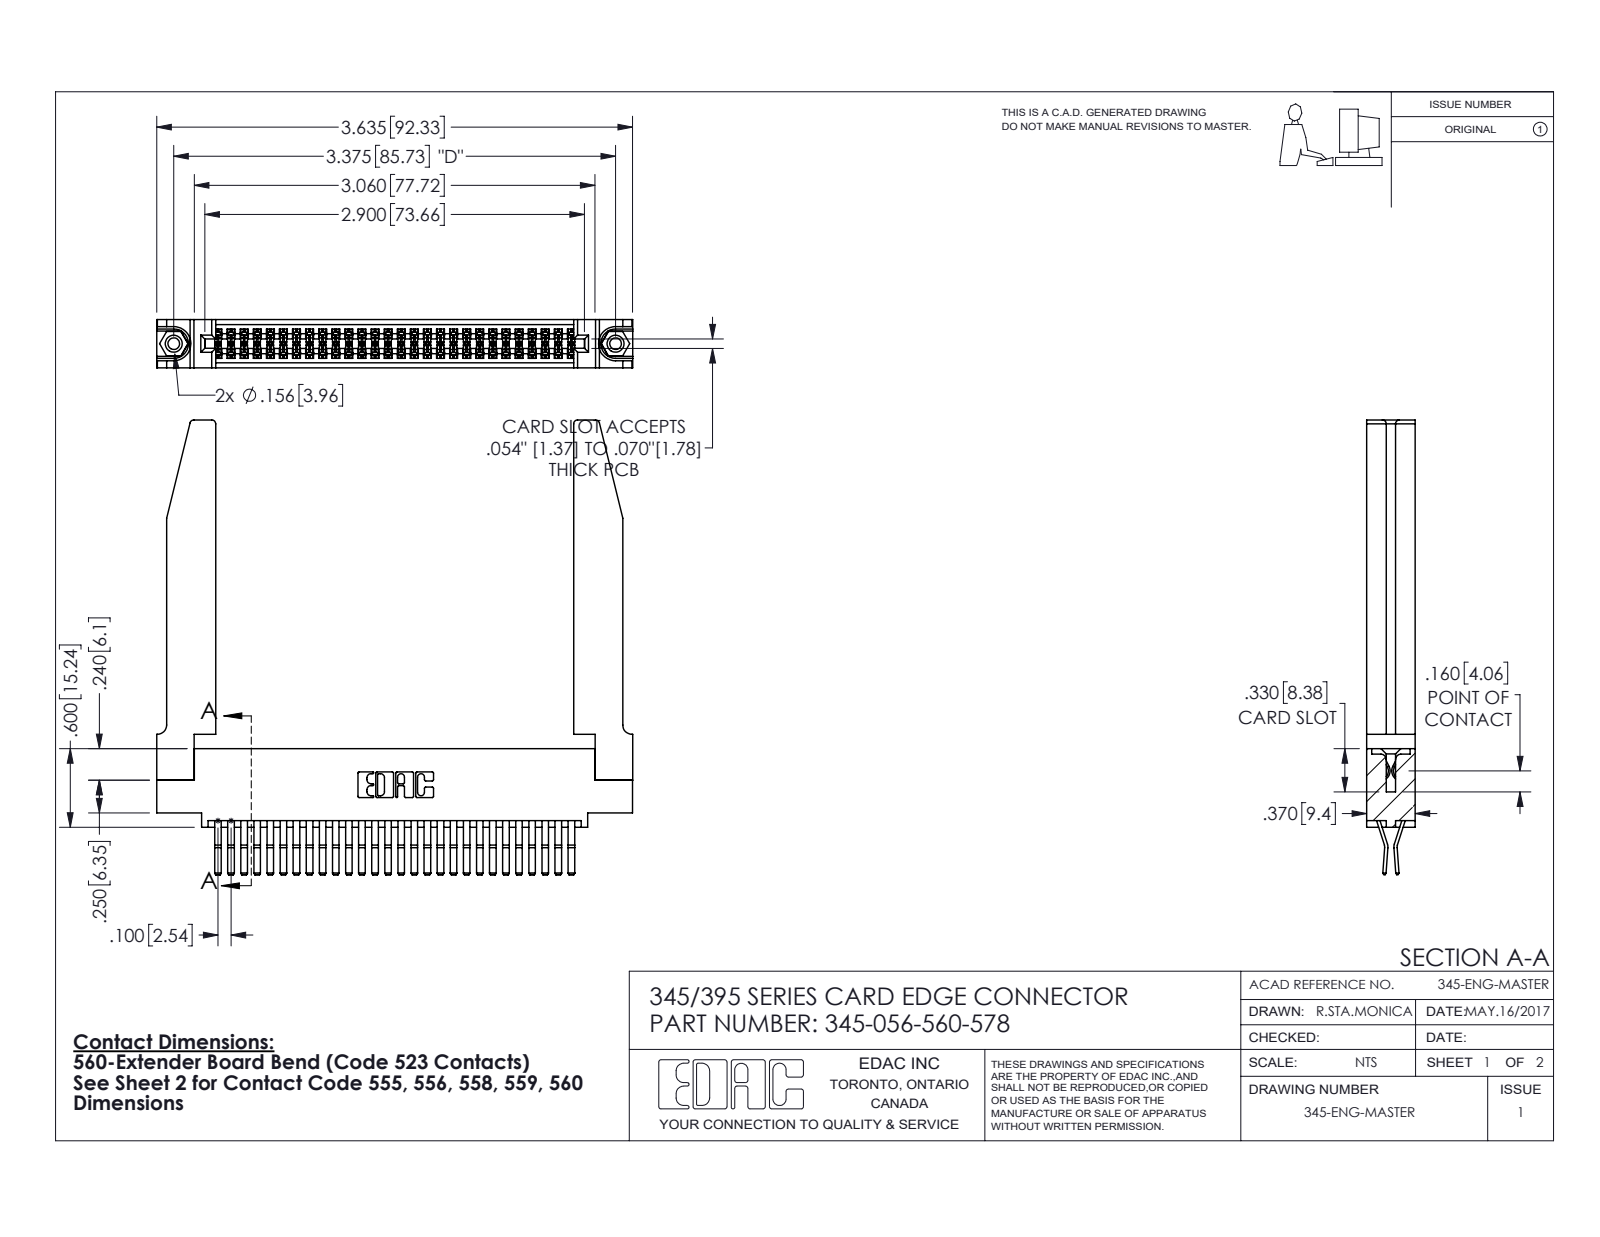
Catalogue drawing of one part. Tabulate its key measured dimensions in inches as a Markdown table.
| quantity | value |
| --- | --- |
| part name | 345-250-001_345-250-001-102; 345-220-078_345-220-078; 345-292-001_560 Tail; 345-056-560-578 (+1 more) |
| STEP written by | SolidWorks 2016 (CONFIG_CONTROL_DESIGN) |
| units | inches |
| bodies | 61 solids, 3276 faces (2074 planar, 1150 cylindrical, 52 other) |
| overall size | 3.636 × 3.472 × 0.37 |
| volume | 1.032 in³ |
| surface area | 32.72 in² |
| round holes (diameter × count) | 0.089 × 2, 0.125 × 2, 0.156 × 2, 0.064 × 1 |
| round bosses / shafts (diameter × count) | 0.155 × 2 |
| partial cylindrical surfaces (radius × count) | 0.006 × 85, 0.01 × 22, 0.03 × 8, 0.007 × 6, 0.031 × 6, 0.026 × 3, 0.01 × 2, 0.014 × 2 |
| main face-to-face distances | 0.37, 0.072, 0.298, 0.025, 0.098, 0.272, 0.2, 0.225, 0.148, 0.15 |
| hole center spacings | 0.27, 3.14, 3.375 |
